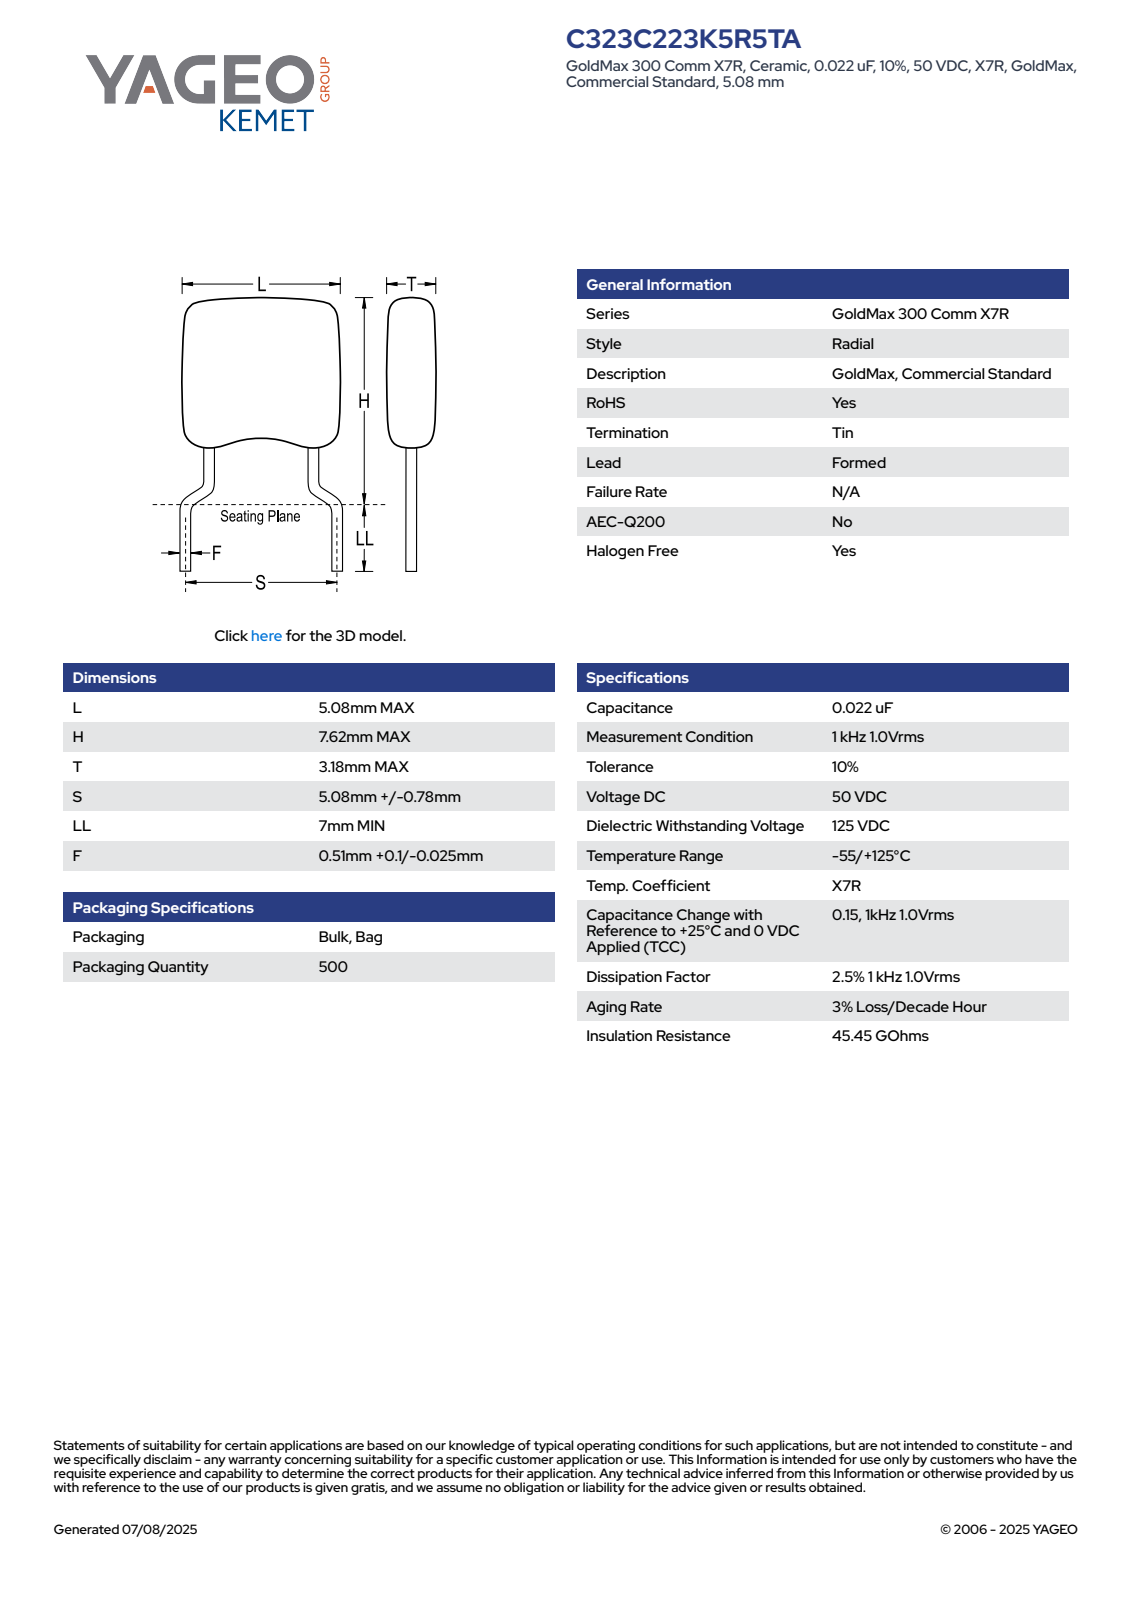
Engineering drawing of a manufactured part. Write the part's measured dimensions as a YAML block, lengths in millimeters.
part_name: "CCRC323_L5.08H7.62T3.18S5.08LL7F0.61"
step_written_by: "SolidWorks 2014 (AUTOMOTIVE_DESIGN)"
units: millimeters
bodies: {solids: 4, faces: 109, planar: 68, cylindrical: 22, other: 19}
overall_size: [14.62, 5.69, 3.19]
volume: 76
surface_area: 134
round_bosses_or_shafts:
  - {diameter: 0.61, count: 6}
partial_cylinders:
  - {radius: 0.75, count: 8}
  - {radius: 1, count: 2}
face_to_face_distances: [3.18, 5.08, 4.81, 9.81, 14.62, 3.19, 0.43, 12.45, 2.64, 2.17]
